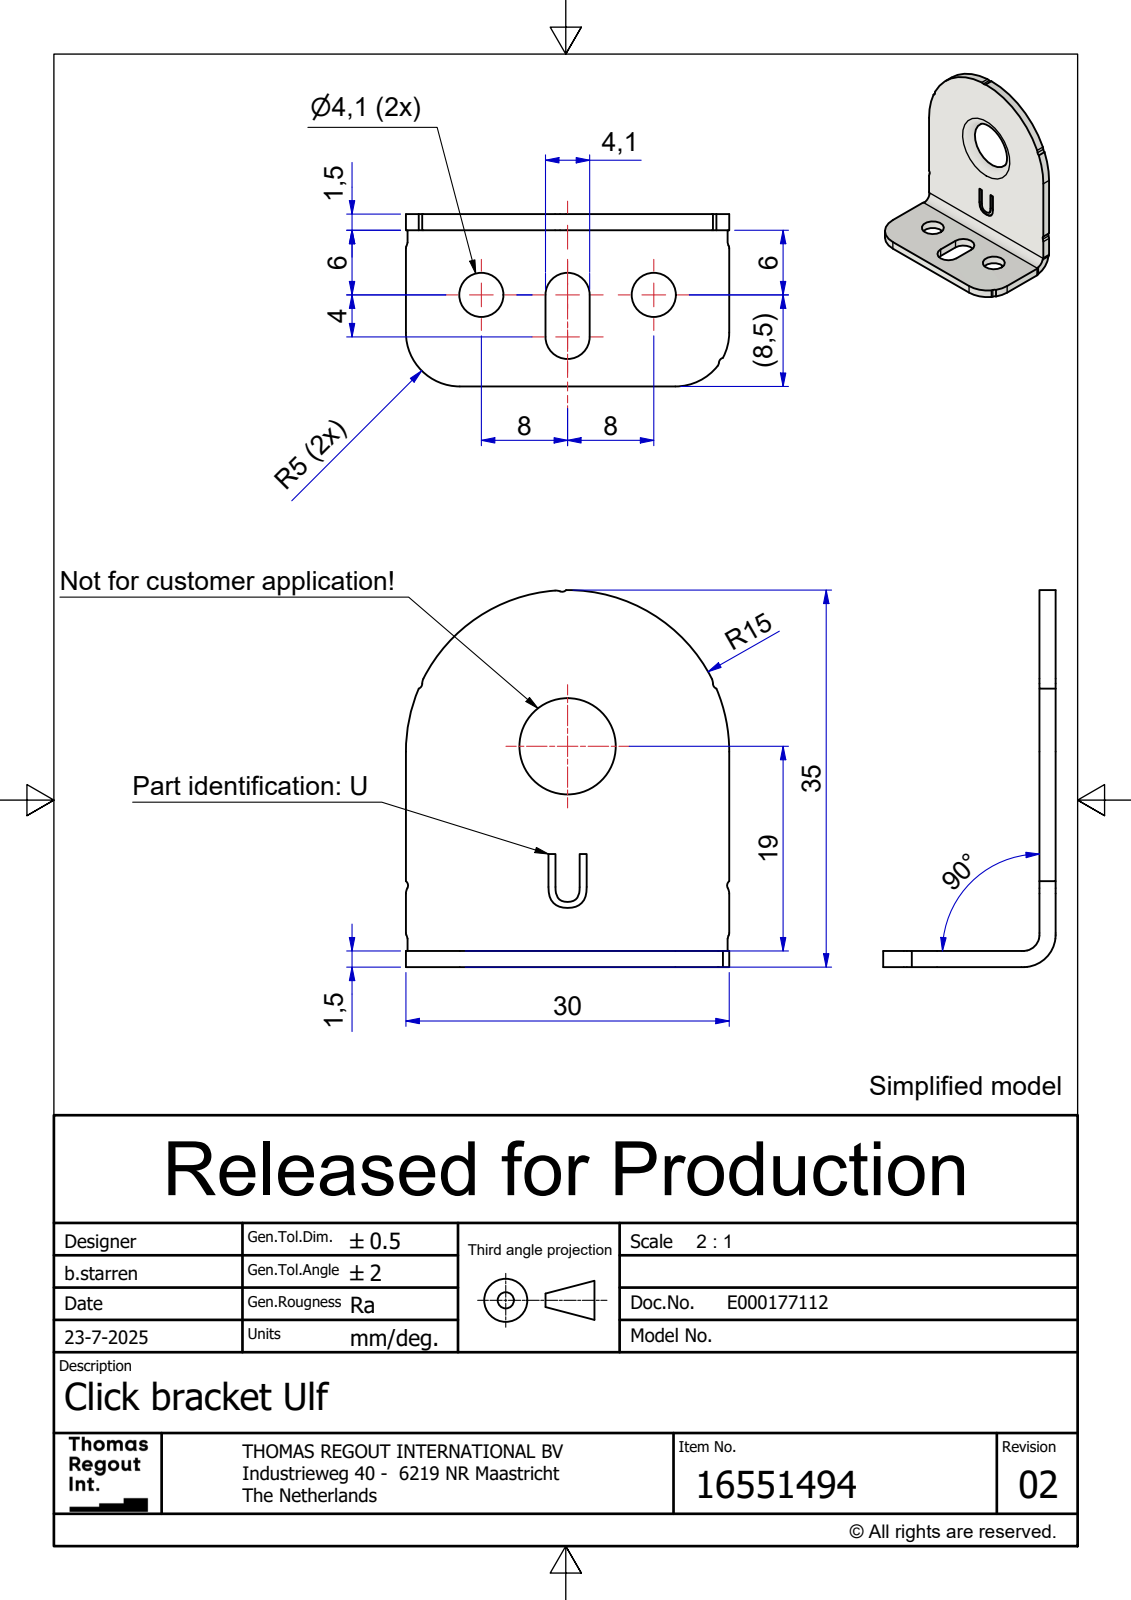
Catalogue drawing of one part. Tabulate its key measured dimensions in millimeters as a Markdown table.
| quantity | value |
| --- | --- |
| part name | E000173777 |
| STEP written by | Autodesk Inventor 2022 (AUTOMOTIVE_DESIGN) |
| units | millimeters |
| bodies | 1 solid, 64 faces (22 planar, 33 cylindrical, 9 other) |
| overall size | 35 × 30 × 16 |
| volume | 1 823 mm³ |
| surface area | 2 763 mm² |
| round holes (diameter × count) | 4.1 × 2 |
| partial cylindrical surfaces (radius × count) | 0.5 × 15, 1 × 5, 2.05 × 2, 5 × 2, 1.5 × 1, 3 × 1, 15 × 1 |
| main face-to-face distances | 1.5, 30, 16, 14.5, 12.95, 17.05, 29.85, 12.8, 16.9, 1.4 |
| hole center spacings | 16 |
